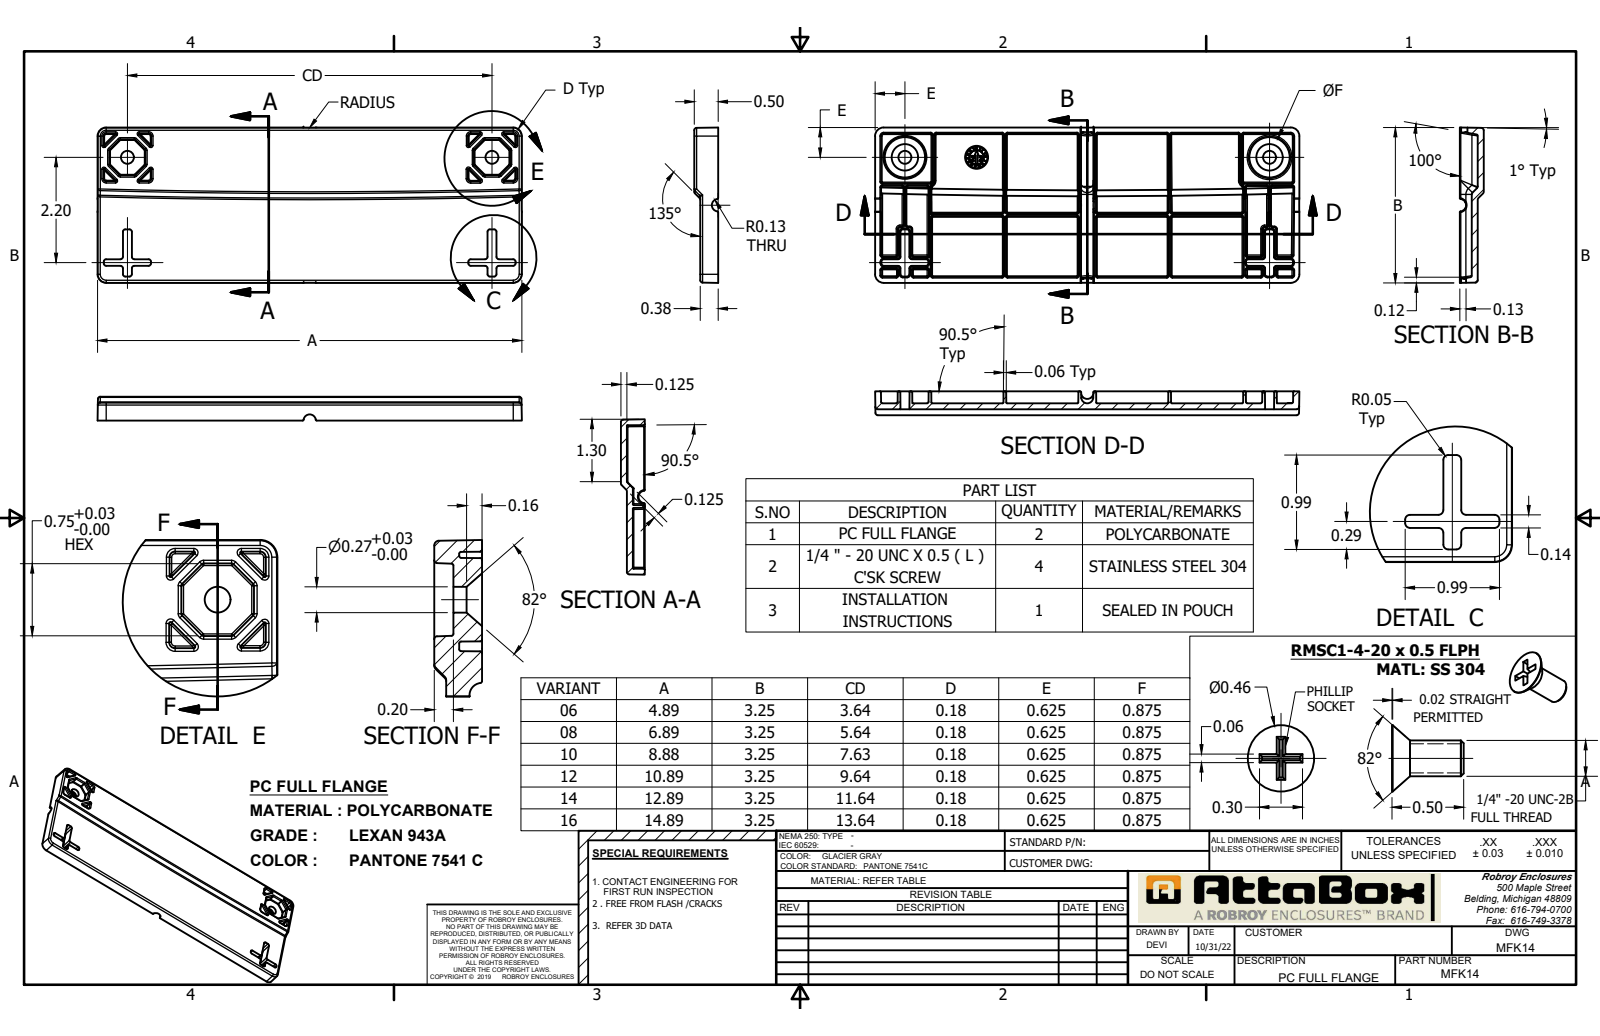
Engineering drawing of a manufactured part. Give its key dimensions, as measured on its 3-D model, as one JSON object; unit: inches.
{"part_name": "MFK14_Default", "step_written_by": "SolidWorks 2023 (CONFIG_CONTROL_DESIGN)", "units": "inches", "bodies": {"solids": 1, "faces": 1195, "planar": 334, "cylindrical": 397, "other": 464}, "overall_size": [12.89, 3.25, 0.5], "volume_in3": 7.293, "surface_area_in2": 127.7, "round_holes": [[0.27, 2]], "partial_cylinders_radius": [[0.02, 122], [0.03, 117], [0.05, 6], [0.125, 3], [0.12, 1], [0.129, 1], [0.129, 1], [0.13, 1]], "face_to_face_distances": [0.25, 0.125, 0.125, 0.5, 0.375, 1.33, 1.731, 2.569, 5.454, 2.885], "hole_center_spacings": [11.64]}
